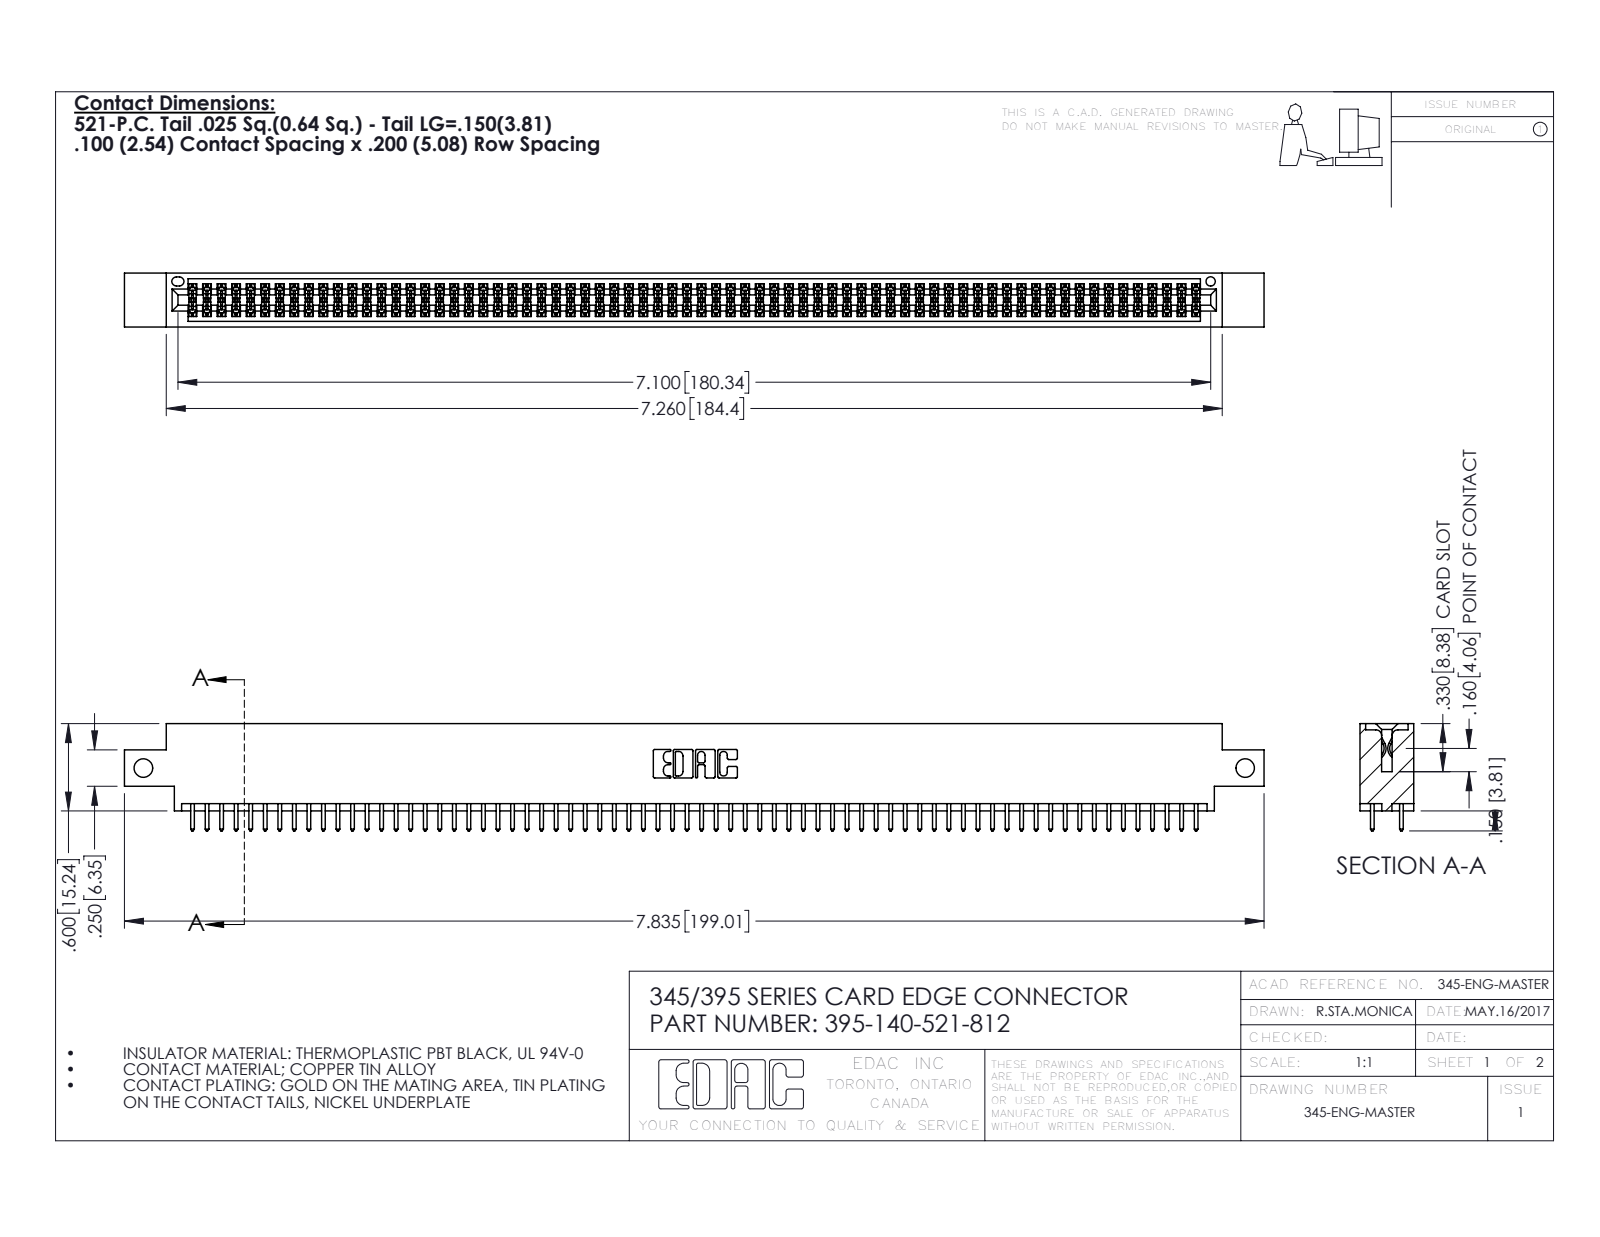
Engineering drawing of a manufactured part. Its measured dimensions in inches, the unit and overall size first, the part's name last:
Units: inches
Overall size (bounding box): 7.835 × 0.737 × 0.37
Round holes (diameter × count): ⌀0.128 ×2, ⌀0.064 ×1
Partial cylindrical surfaces — rounded edges, fillets, slot ends (radius × count): R0.006 ×210, R0.01 ×140, R0.01 ×22, R0.007 ×6, R0.031 ×6, R0.026 ×3, R0.014 ×2, R0.019 ×2
Main face-to-face distances: 0.072, 0.298, 0.2, 0.37, 0.098, 0.272, 0.025, 0.225, 0.175, 0.149
Hole centre spacings: 7.575
Volume: 1.18 in³ · Surface area: 44.57 in²
Bodies: 141 solids, 7130 faces (4704 planar, 2426 cylindrical, 0 other)
Part name (STEP PRODUCT): 395-140-521-812; 345 Part_0.170 Offset - Side Mount; 345-292-001_345-293-121
STEP written by: SolidWorks 2016 (CONFIG_CONTROL_DESIGN)
